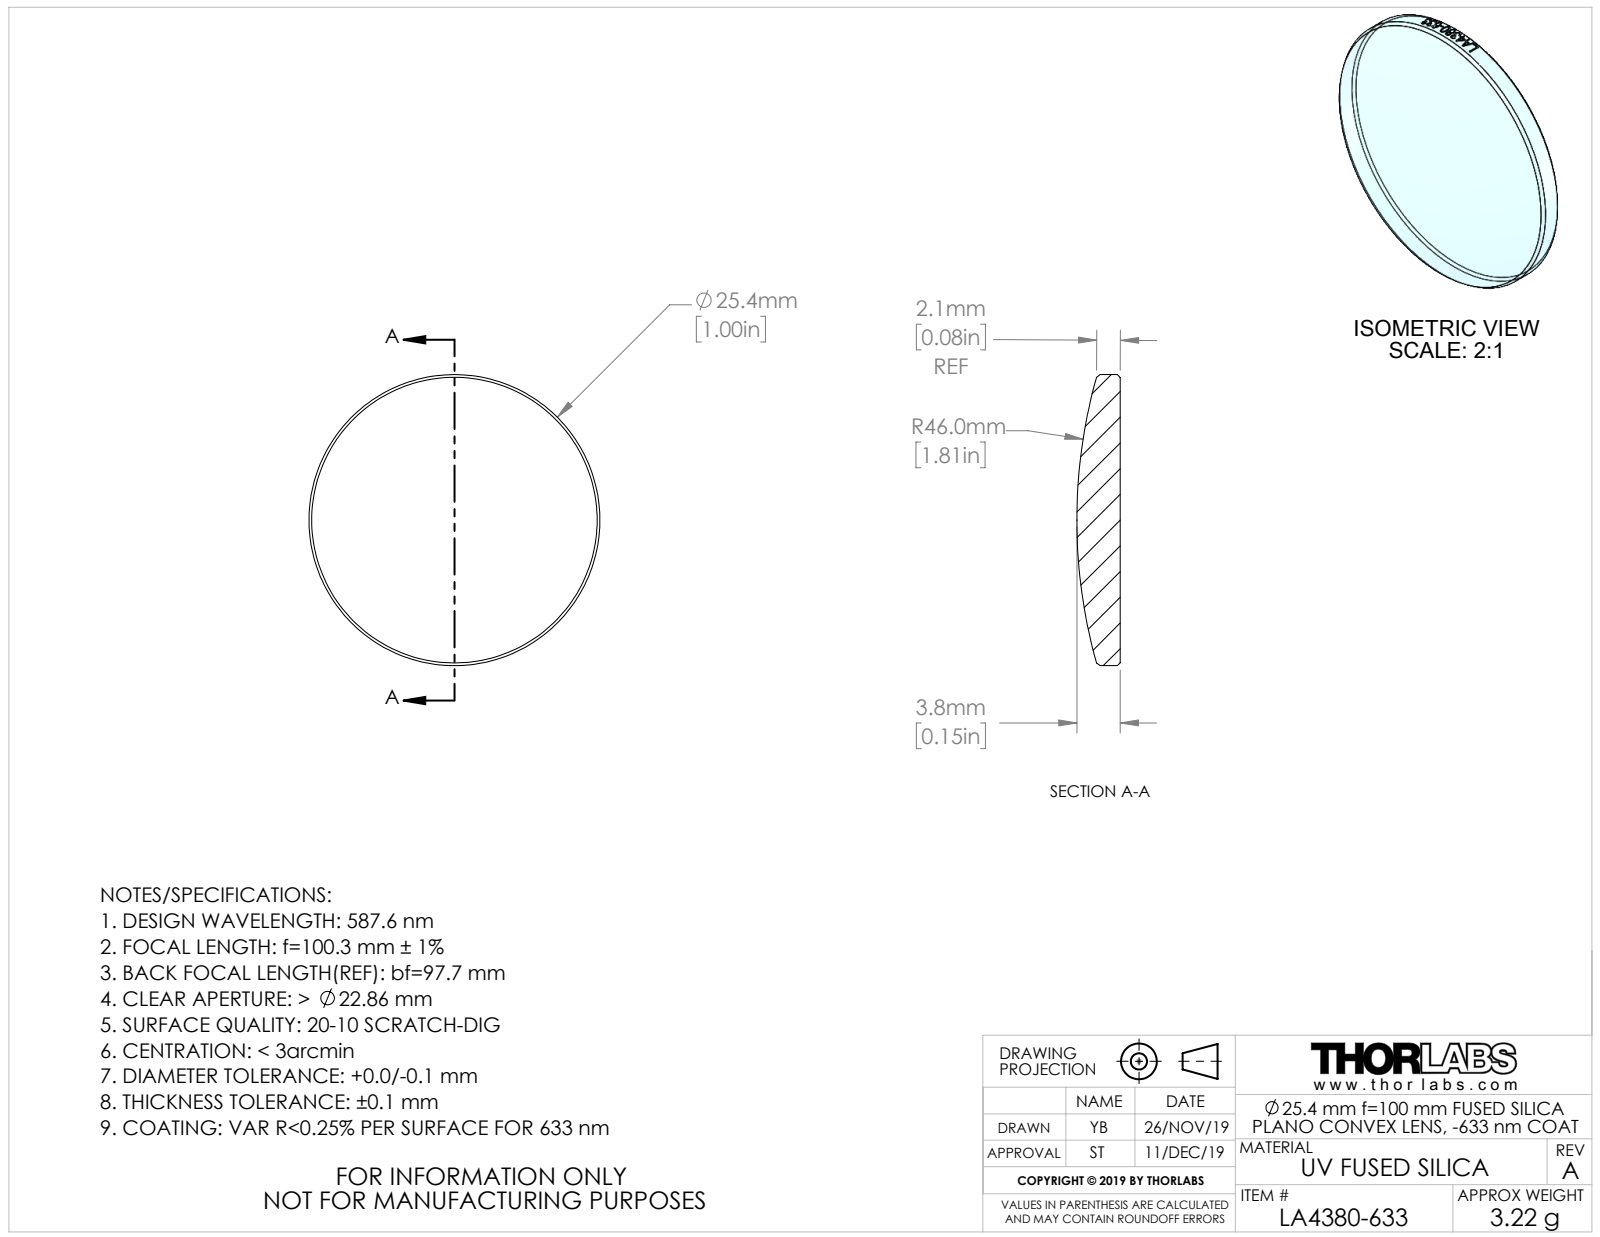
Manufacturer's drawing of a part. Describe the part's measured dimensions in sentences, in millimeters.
The part is named "CTN014992-999; CTN015011". Its 3-D file was written by "SolidWorks 2018 (AUTOMOTIVE_DESIGN)". It is 1 solid with 29 faces: 1 planar, 22 cylindrical and 6 other. Overall it measures 25.4 by 25.4 by 3.78 millimeters. Its volume is 1 463 cubic millimeters and its surface area 1 163 square millimeters. Round bosses or shafts: 1 of diameter 25.4.
